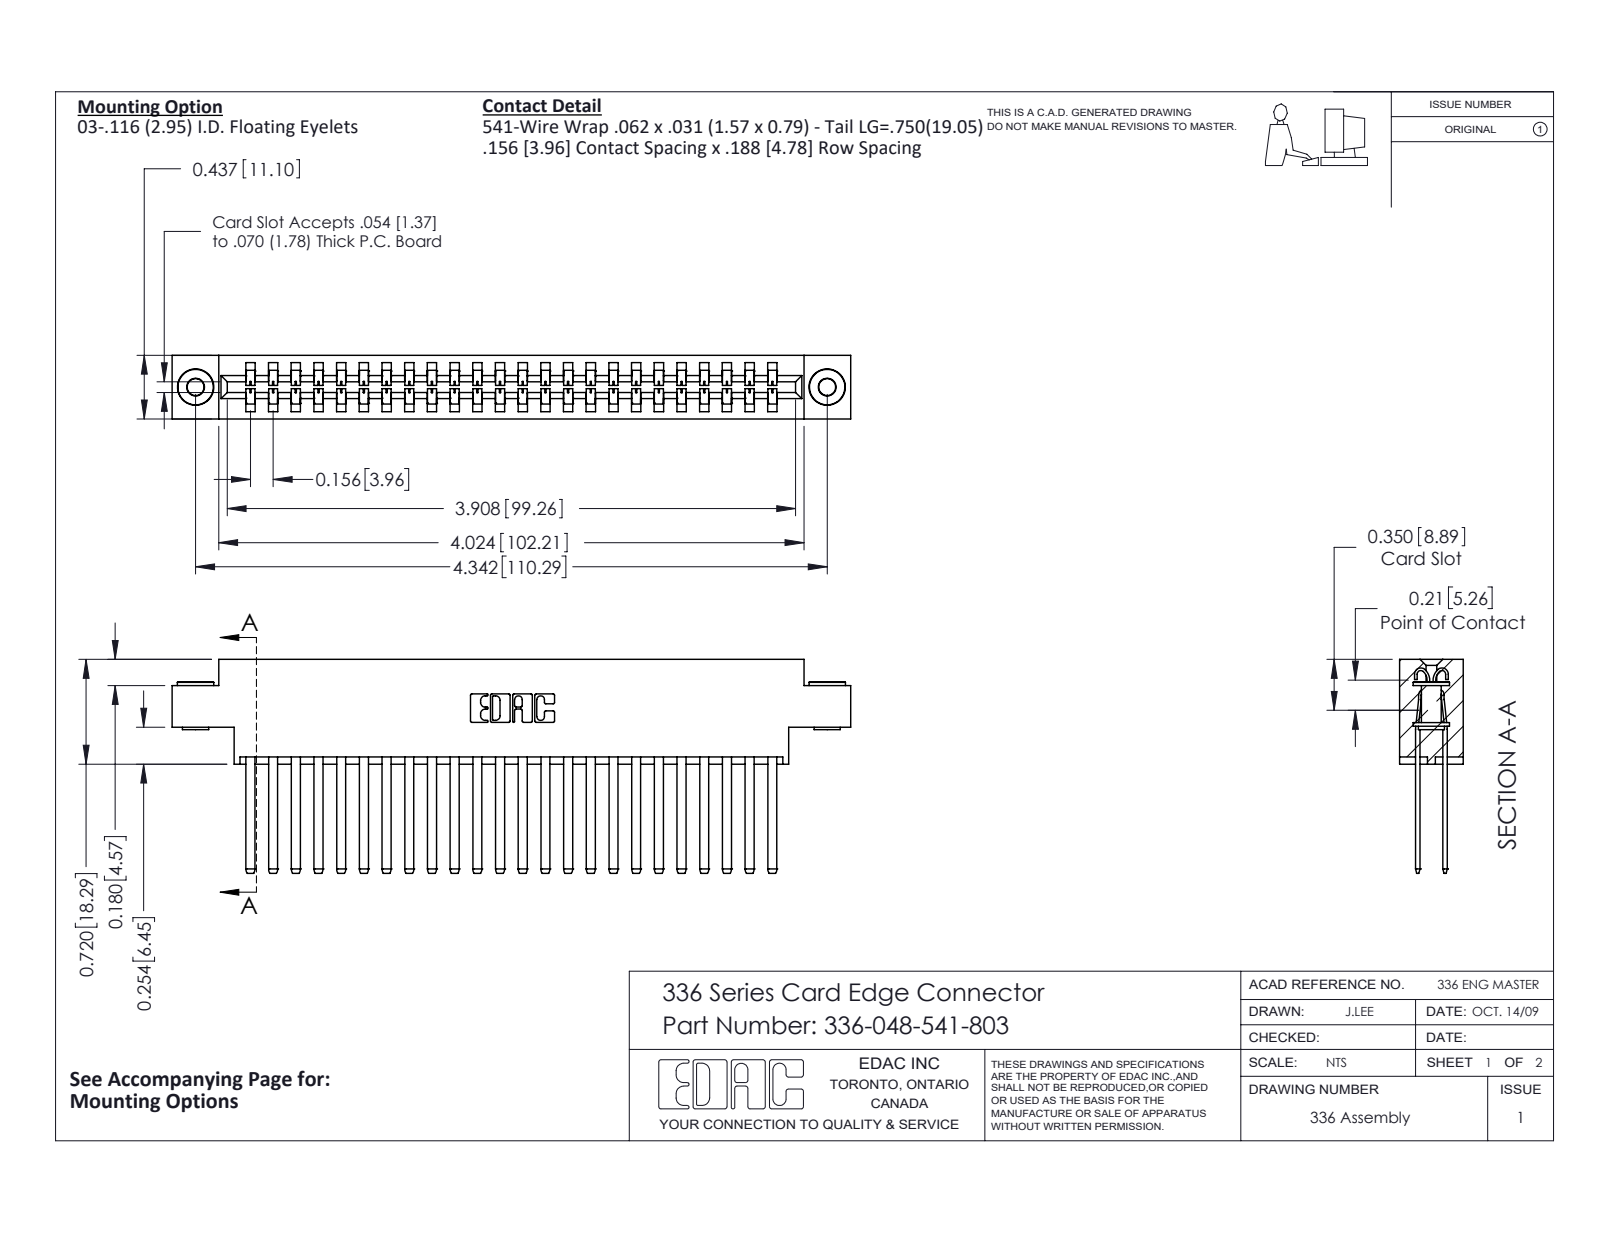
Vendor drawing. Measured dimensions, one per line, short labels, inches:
name: 336-290-001_336-290-541; 336-048-541-803; 345-250-002_345-250-002-102; 336 Part_Offset - .156 Dia - TH
written by: SolidWorks 2020 (CONFIG_CONTROL_DESIGN)
unit: in
bodies: 51 solids, 2172 faces (1332 planar, 832 cylindrical, 8 other)
size: 4.665 × 1.47 × 0.437
volume: 1.082 in³; area: 35.07 in²
holes: 2× ⌀0.116, 2× ⌀0.156
bosses: 2× ⌀0.25, 2× ⌀0.18, 2× ⌀0.136
rounds: 96× R0.004, 48× R0.056, 22× R0.01, 6× R0.007, 6× R0.031, 4× R0.022, 4× R0.04, 3× R0.026
face distances: 0.188, 0.031, 0.328, 0.14, 0.297, 0.109, 0.437, 0.033, 0.181, 0.156
hole spacings: 4.342
